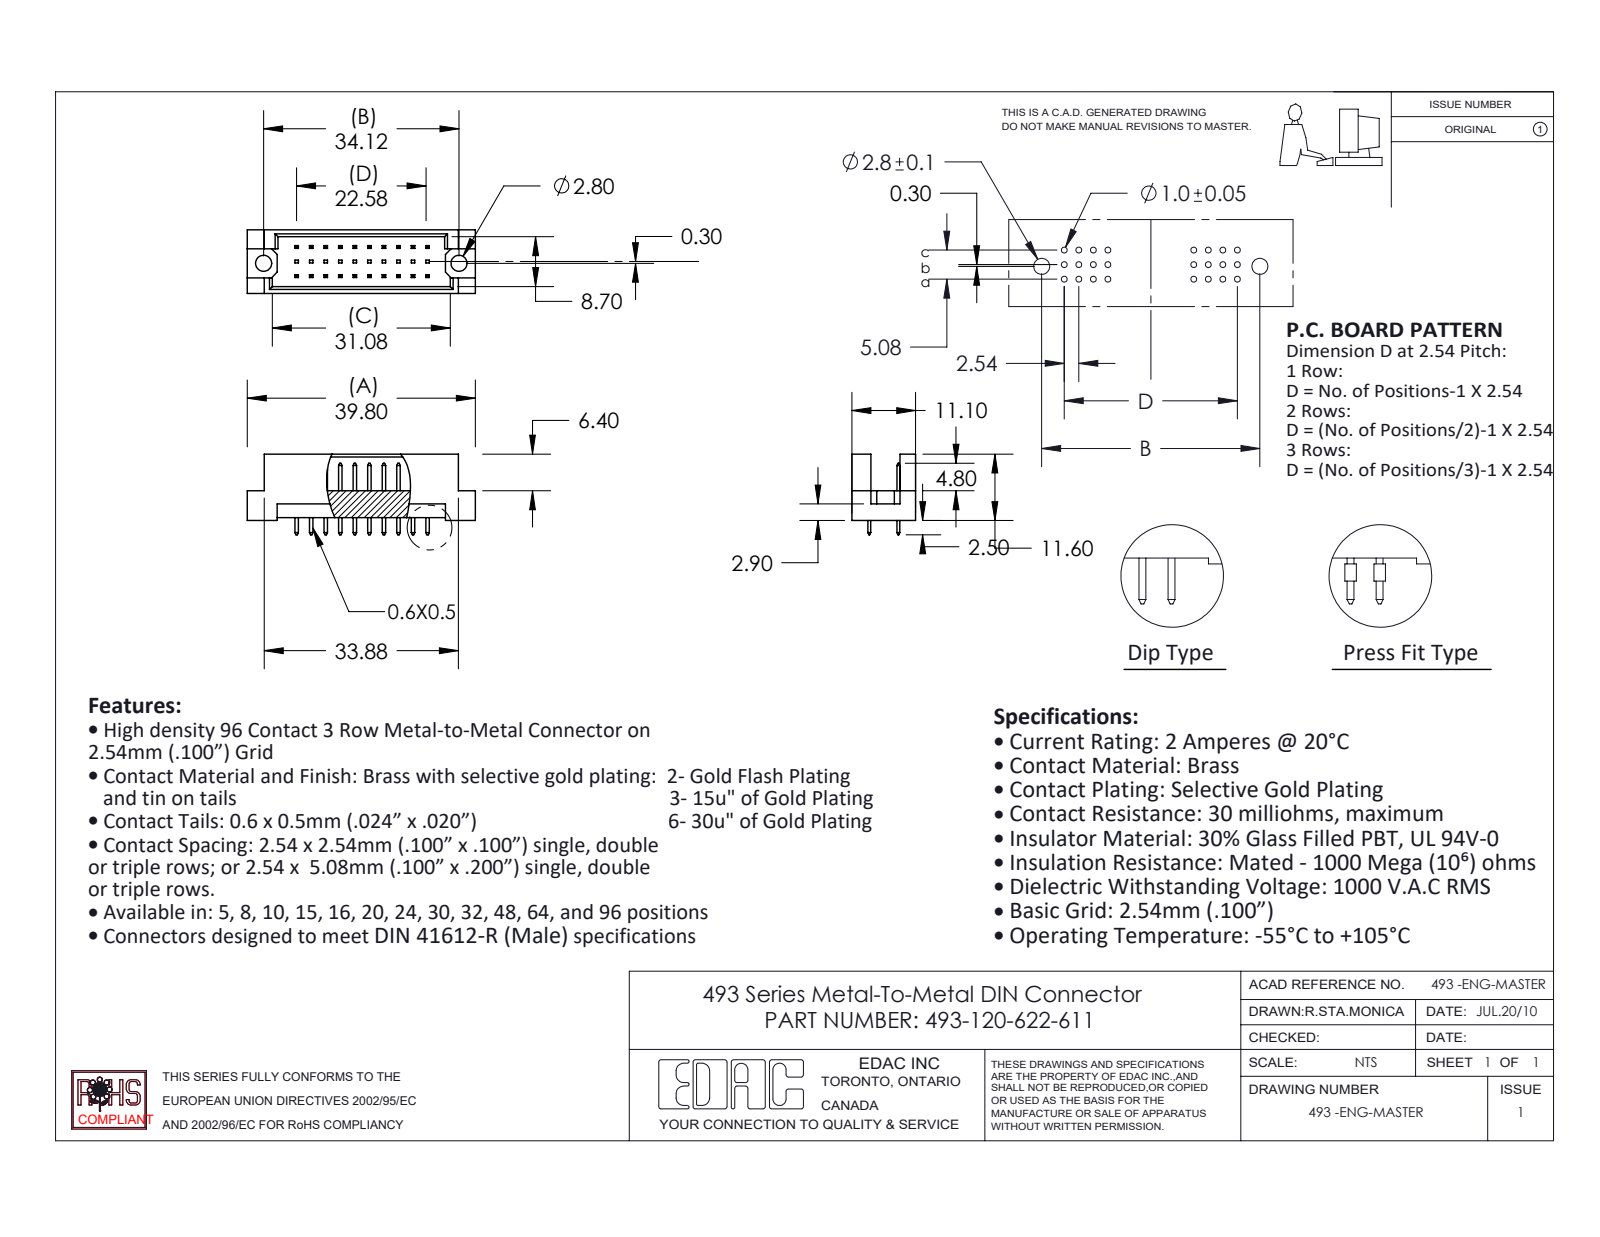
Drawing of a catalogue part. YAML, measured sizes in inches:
part_name: "493-120-622-611; 493-290_22; 493 Part_30"
step_written_by: "SolidWorks 2020 (CONFIG_CONTROL_DESIGN)"
units: inches
bodies: {solids: 21, faces: 452, planar: 448, cylindrical: 4, other: 0}
overall_size: [1.567, 0.555, 0.437]
volume: 0.149
surface_area: 5.084
round_holes:
  - {diameter: 0.11, count: 2}
face_to_face_distances: [0.047, 0.39, 0.2, 0.437, 0.1, 0.02, 0.343, 0.185, 0.109, 0.128]
hole_center_spacings: [1.343]
